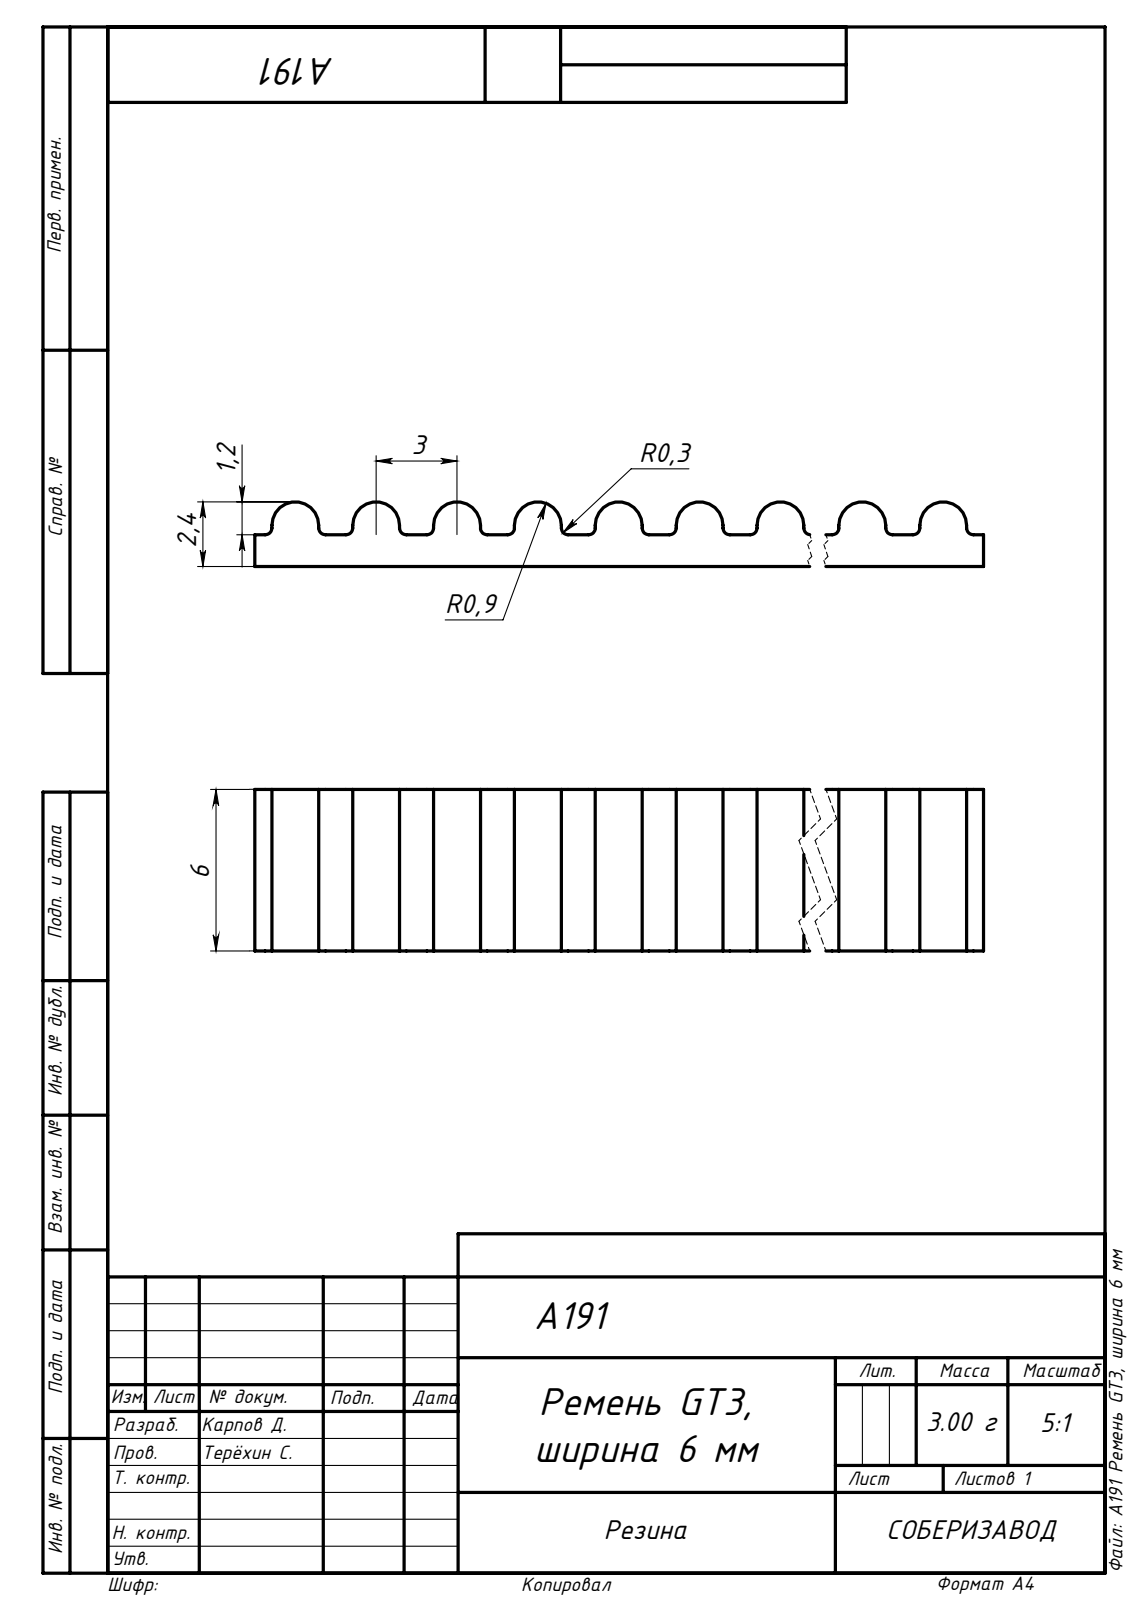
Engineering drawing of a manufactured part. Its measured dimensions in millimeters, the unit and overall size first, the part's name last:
Units: millimetres
Overall size (bounding box): 102 × 6 × 2.4
Partial cylindrical surfaces — rounded edges, fillets, slot ends (radius × count): R0.25 ×68, R0.87 ×34
Main face-to-face distances: 6, 1.18, 3, 9, 12, 15, 18, 102, 21, 24
Volume: 1 094 mm³ · Surface area: 1 905 mm²
Bodies: 1 solid, 210 faces (108 planar, 102 cylindrical, 0 other)
Part name (STEP PRODUCT): A191 Ремень GT3, ширина 6 мм
STEP written by: SolidWorks 2019 (AUTOMOTIVE_DESIGN)
